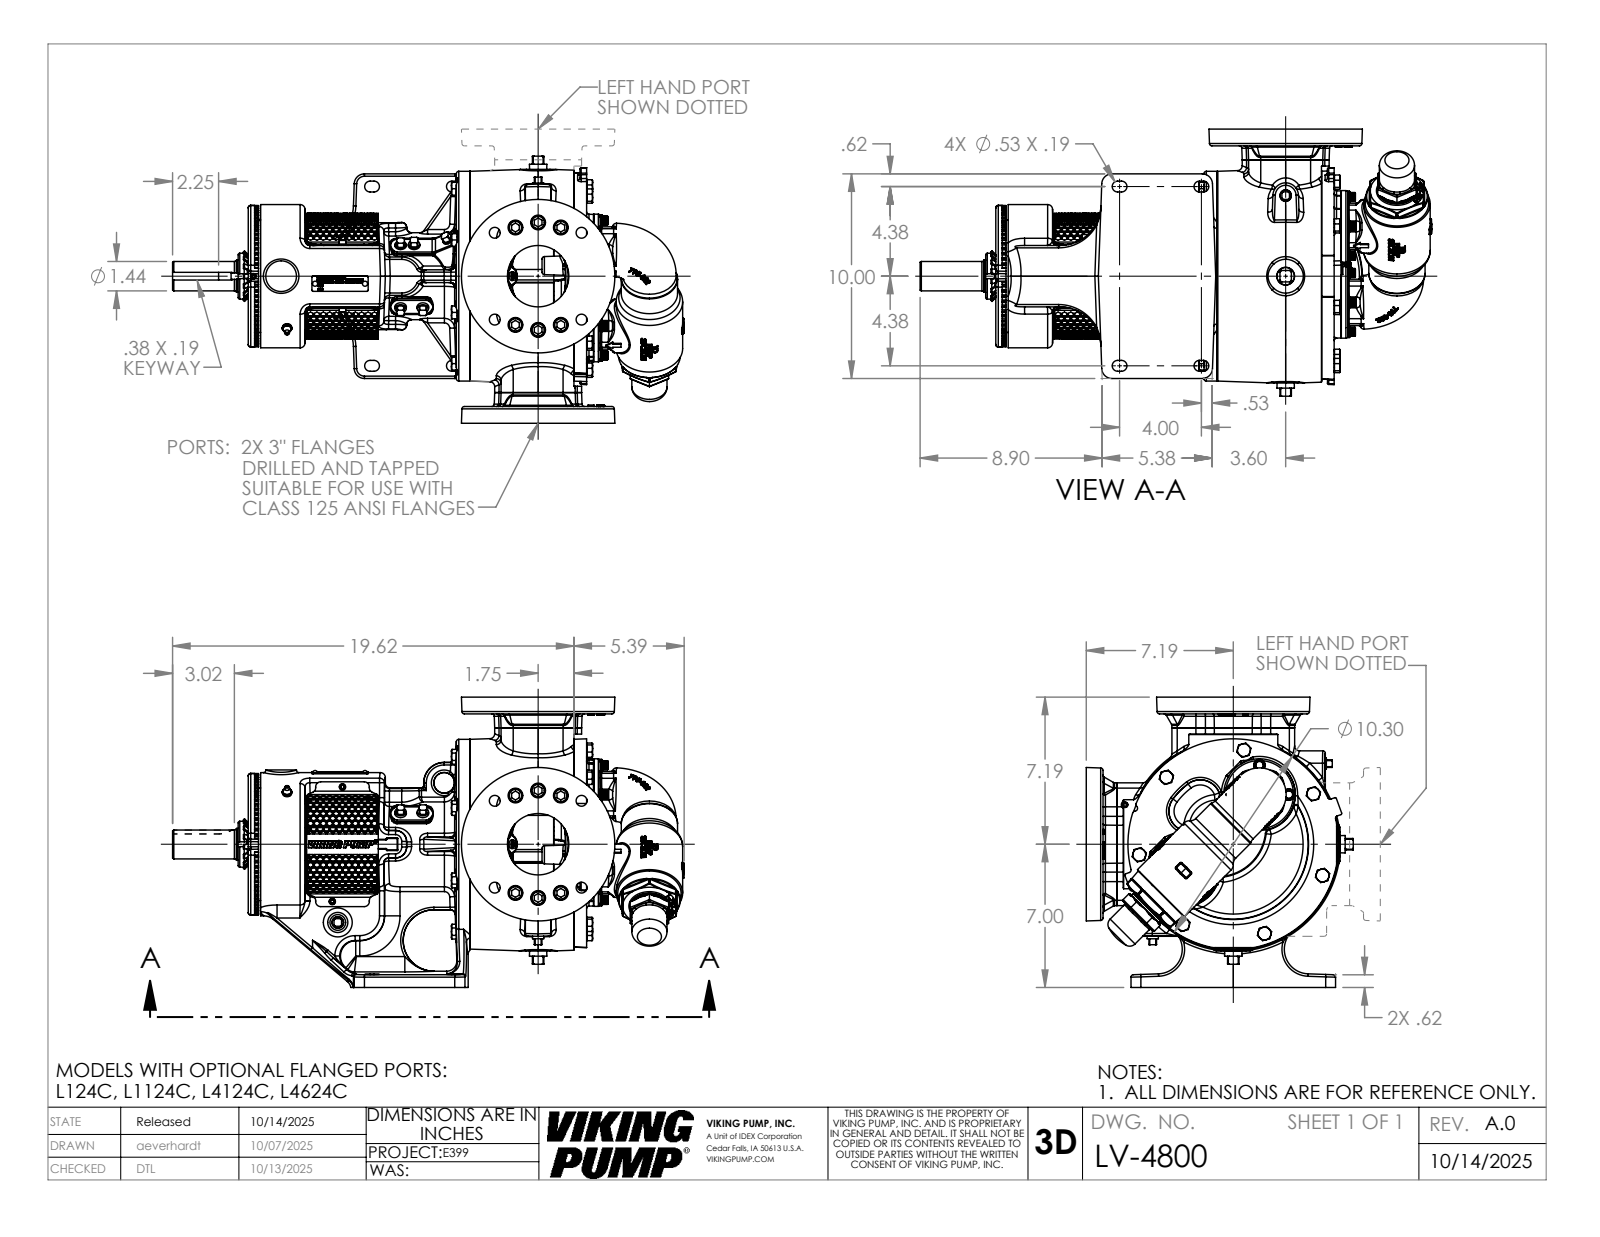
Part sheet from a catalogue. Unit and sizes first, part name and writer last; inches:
Units: inches
Overall size (bounding box): 25.01 × 14.188 × 13.053
Round holes (diameter × count): ⌀0.469 ×12, ⌀0.719 ×12, ⌀0.25 ×9, ⌀0.406 ×8, ⌀0.41 ×8, ⌀0.531 ×8, ⌀1.094 ×8, ⌀0.199 ×6, ⌀0.159 ×3, ⌀0.266 ×2, ⌀0.313 ×2, ⌀3 ×2
Round bosses / shafts (diameter × count): ⌀0.66 ×12, ⌀0.437 ×12, ⌀0.625 ×9, ⌀0.563 ×8, ⌀0.625 ×6, ⌀0.375 ×4, ⌀0.375 ×4, ⌀3.5 ×3
Partial cylindrical surfaces — rounded edges, fillets, slot ends (radius × count): R0.063 ×109, R0.12 ×80, R0.069 ×74, R0.24 ×48, R0.03 ×36, R0.01 ×30, R0.009 ×26, R0.45 ×16
Main face-to-face distances: 14.187, 0.82, 13.792, 3.537, 10.255, 0.5, 2.25, 13.367, 1.382, 0.562
Hole centre spacings: 3, 4.243, 2.625, 1.375, 1.044, 1.136, 2.033, 2.033
Volume: 986.5 in³ · Surface area: 1 506 in²
Bodies: 1 solid, 6237 faces (1945 planar, 1317 cylindrical, 2975 other)
Part name (STEP PRODUCT): LV-4800
STEP written by: SolidWorks 2024 (AUTOMOTIVE_DESIGN)
